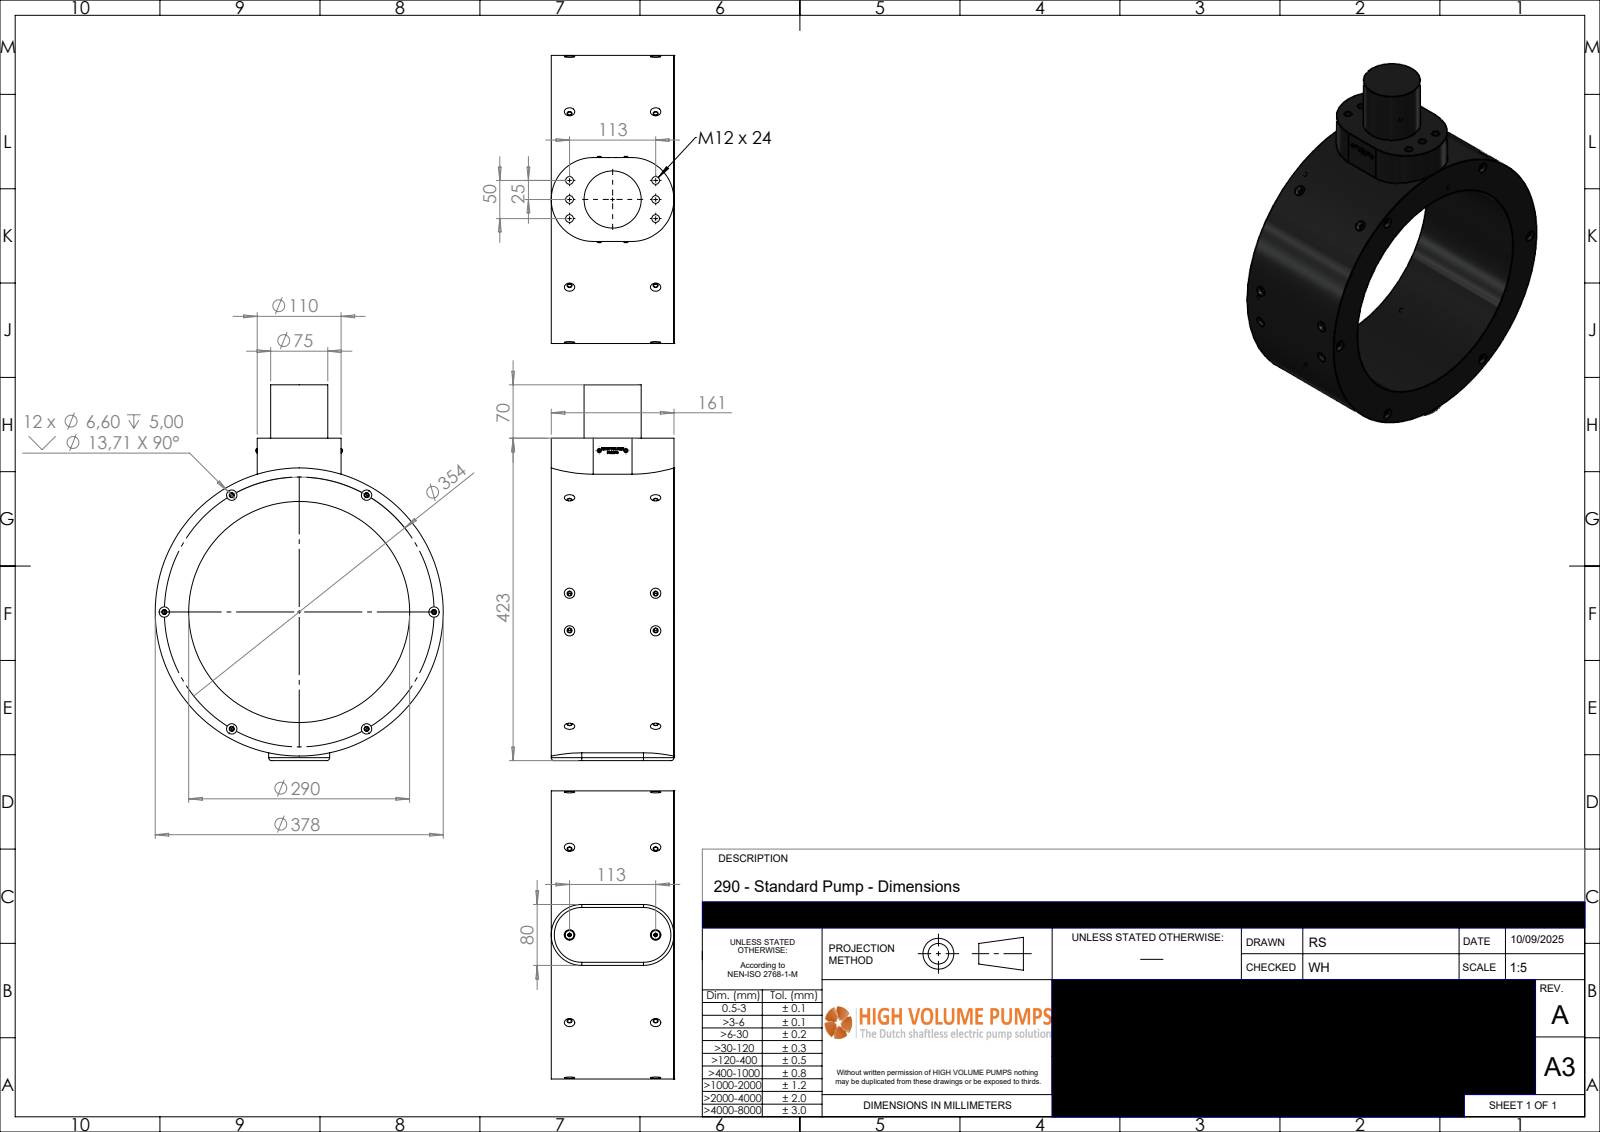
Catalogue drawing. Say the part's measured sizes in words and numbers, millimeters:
The part is named "P-290-030-rev-A-SP". Its 3-D file was written by "SolidWorks 2024 (AUTOMOTIVE_DESIGN)". It is 1 solid with 658 faces: 385 planar, 66 cylindrical and 207 other. Overall it measures 493 by 378 by 161.05 millimeters. Its volume is 8 420 000 cubic millimeters and its surface area 483 822 square millimeters. Round holes: 22 of diameter 5, 6 of diameter 6.6, 6 of diameter 10.2, 2 of diameter 3.5, 1 of diameter 290. Round bosses or shafts: 2 of diameter 11.57, 2 of diameter 5.7, 1 of diameter 378, 1 of diameter 75. Partial cylindrical surfaces (rounded edges, fillets, slot ends): 2 of radius 4, 2 of radius 40, 2 of radius 55. The main face-to-face distances are 161.05, 423, 493, 70, 110, 95, 15, 80, 398, 25. The hole center spacings are 113, 177, 0.36, 25, 115.73, 306.57, 50, 123.57.
